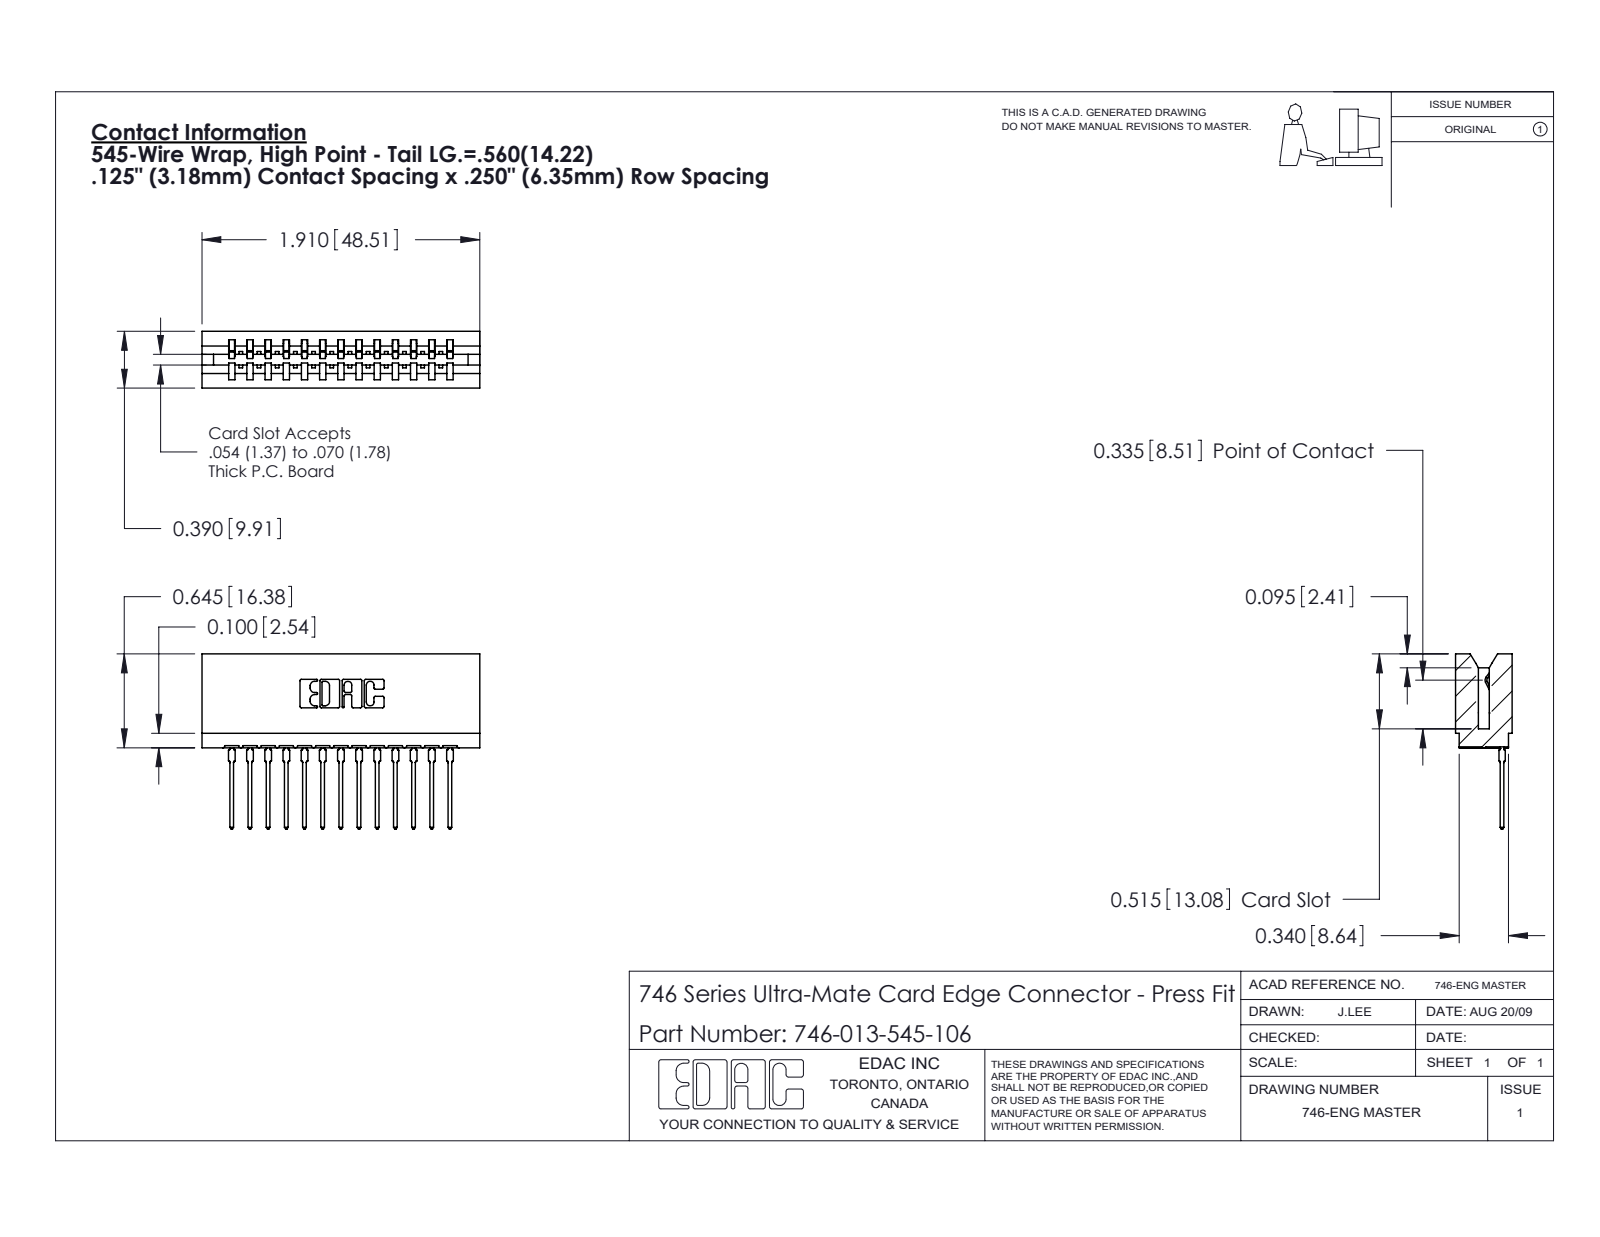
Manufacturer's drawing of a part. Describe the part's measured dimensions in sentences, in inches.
The part is named "746-292-001_545; 746-013-545-106; 746 Part_.515 Slot Depth - 06". Its 3-D file was written by "SolidWorks 2020 (CONFIG_CONTROL_DESIGN)". It is 14 solids with 1502 faces: 875 planar, 289 cylindrical and 338 other. Overall it measures 1.91 by 1.204 by 0.39 inches. Its volume is 0.322 cubic inches and its surface area 11.68 square inches. Partial cylindrical surfaces (rounded edges, fillets, slot ends): 26 of radius 0.021, 22 of radius 0.01, 14 of radius 0.015, 6 of radius 0.007, 6 of radius 0.031, 4 of radius 0.005, 4 of radius 0.011, 3 of radius 0.026. The main face-to-face distances are 0.25, 0.333, 0.057, 0.5, 0.39, 0.125, 0.125, 0.292, 0.75, 0.042.
